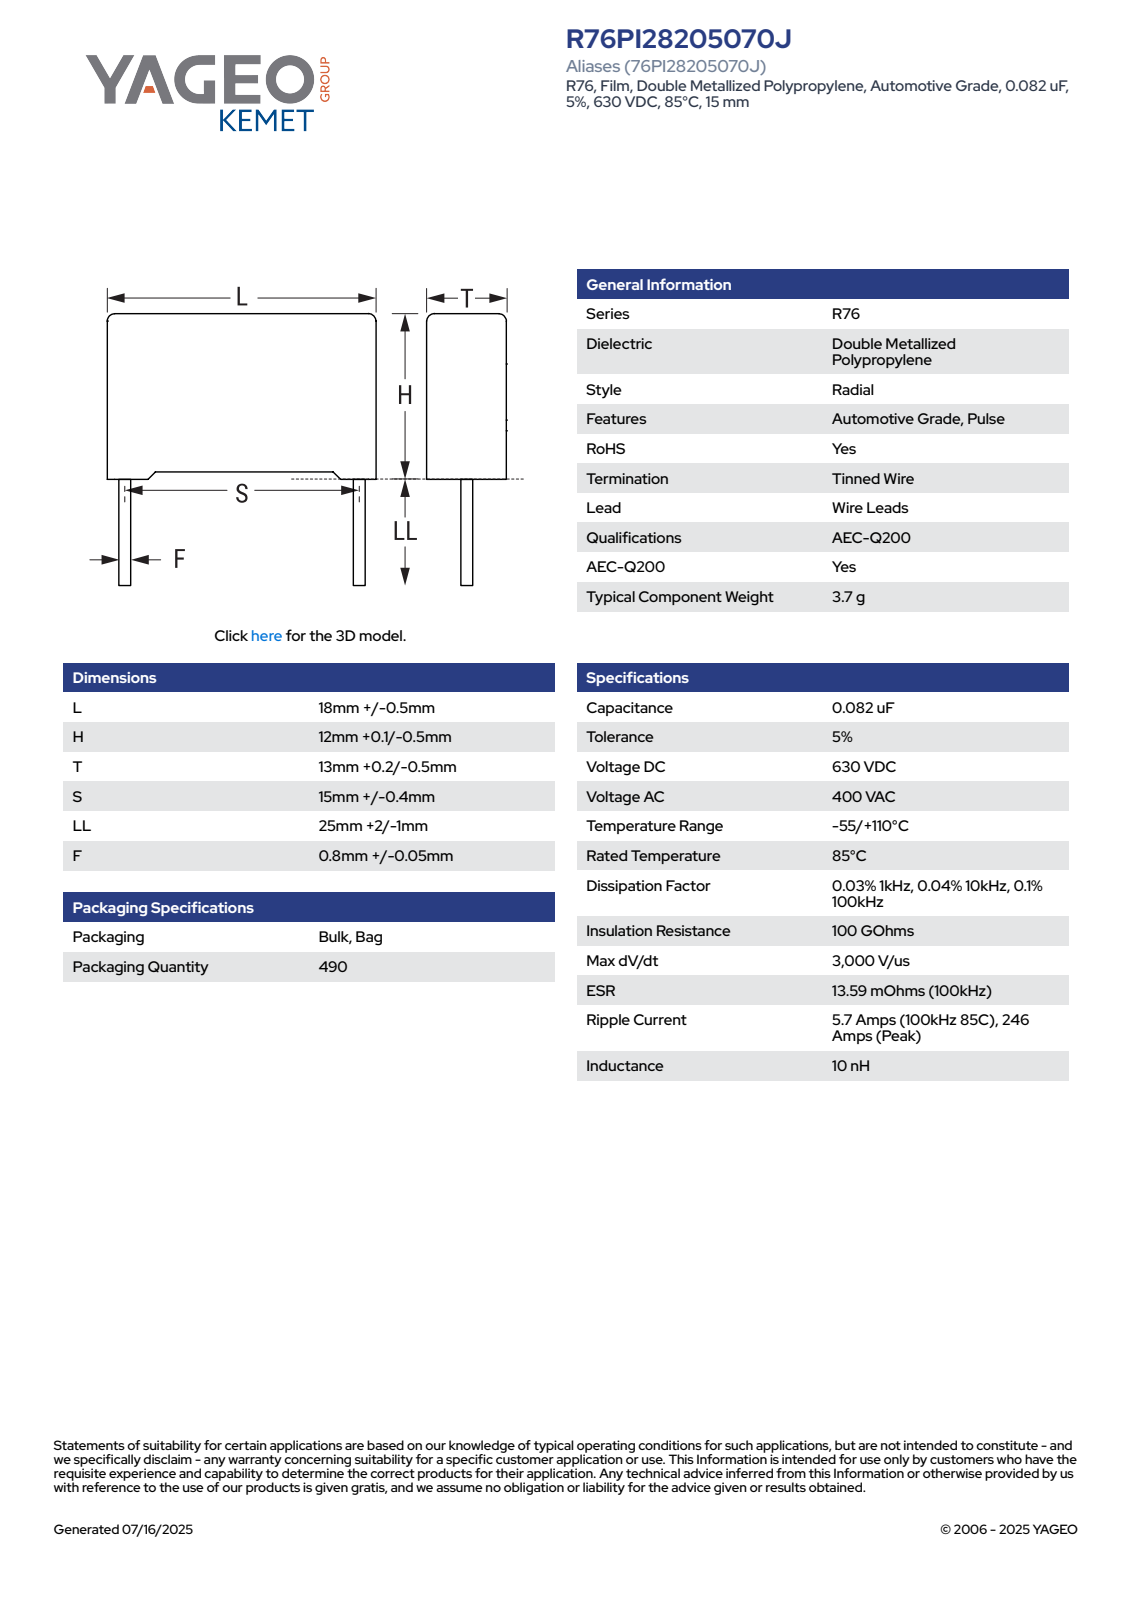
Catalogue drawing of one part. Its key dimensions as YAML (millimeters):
part_name: "CFR_RB2_18X12X13_L18.5H12.1T13.2S15LL27F0.85"
step_written_by: "SolidWorks 2021 (AUTOMOTIVE_DESIGN)"
units: millimeters
bodies: {solids: 4, faces: 85, planar: 77, cylindrical: 8, other: 0}
overall_size: [39.1, 18.5, 13.21]
volume: 2822
surface_area: 1441
round_bosses_or_shafts:
  - {diameter: 0.85, count: 2}
partial_cylinders:
  - {radius: 0.5, count: 4}
face_to_face_distances: [13.2, 11.35, 18.5, 0.62, 0.75, 12.1, 17.88, 12.58, 0.42, 0.33]
